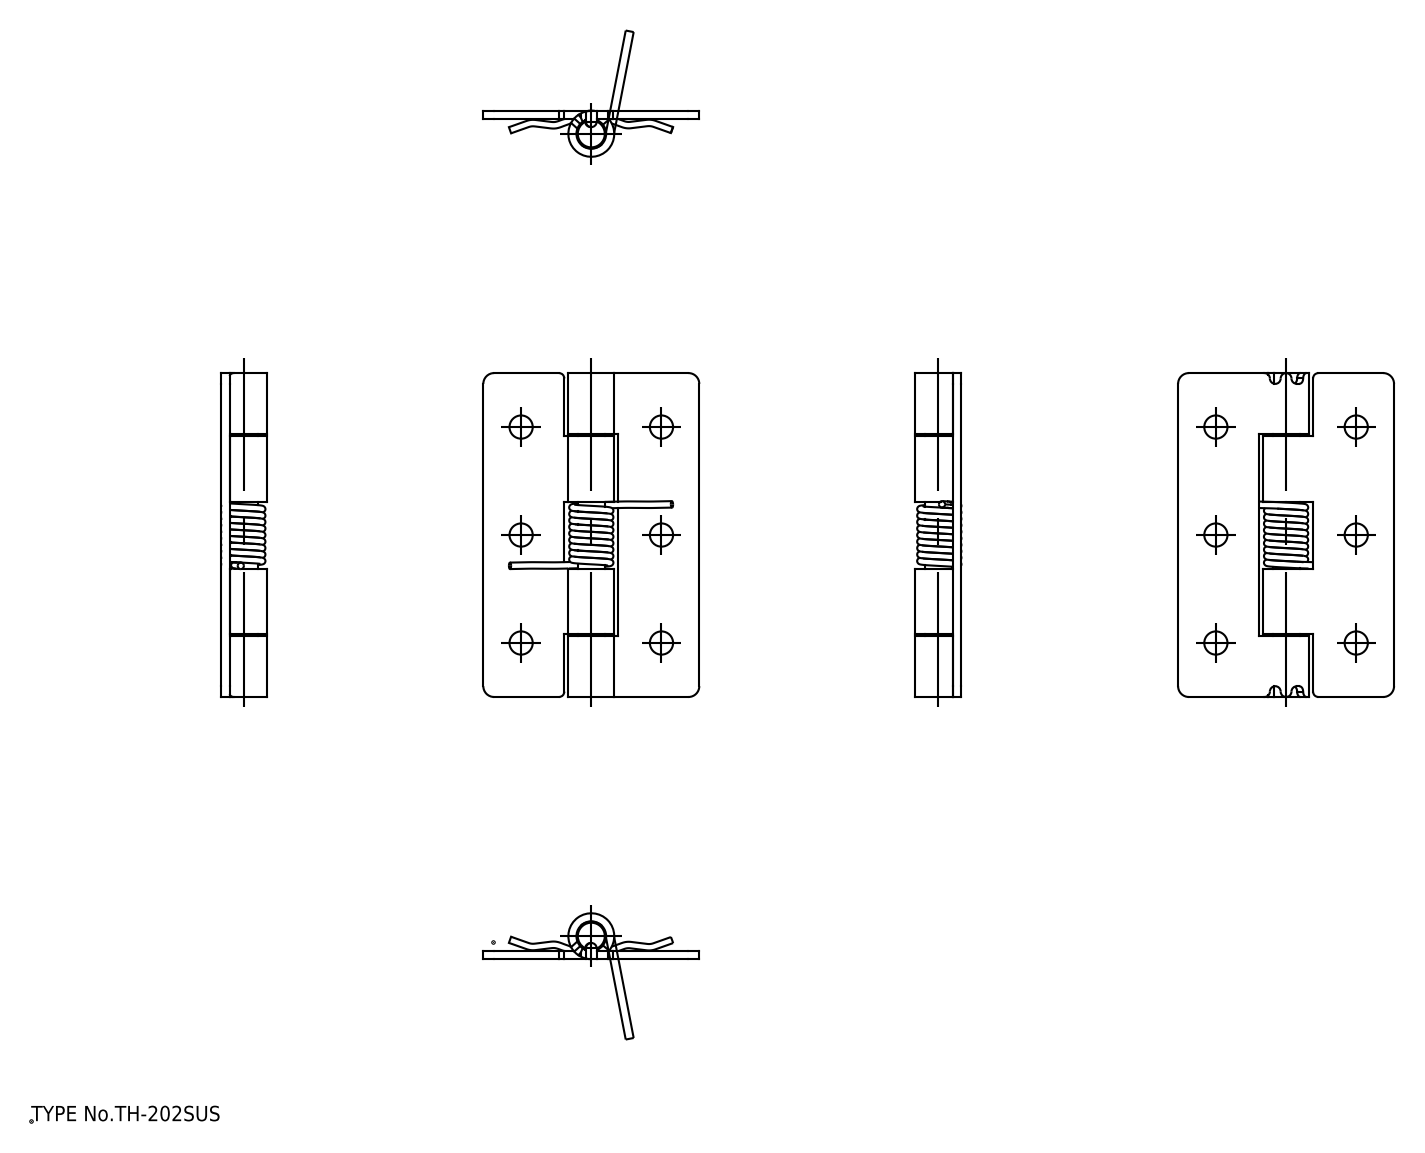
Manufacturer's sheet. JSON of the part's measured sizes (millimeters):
{"part_name": "シャフト; ヒンジピースA; ヒンジピースB; スプリング", "step_written_by": "spGate 20.6.3 (****-****-****-****) (AUTOMOTIVE_DESIGN)", "units": "millimeters", "bodies": {"solids": 4, "faces": 88, "planar": 38, "cylindrical": 42, "other": 8}, "overall_size": [60, 40, 8.56], "volume_mm3": 5547, "surface_area_mm2": 8260, "round_holes": [[4.3, 6], [5.5, 1]], "round_bosses_or_shafts": [[8.5, 1], [5, 1]], "partial_cylinders_radius": [[1, 15], [2, 4]], "face_to_face_distances": [1.5, 15, 25, 40, 11.35, 48.65, 11.6, 48.4, 37.05, 23.8], "hole_center_spacings": [20, 32.8, 26, 40, 47.71]}
